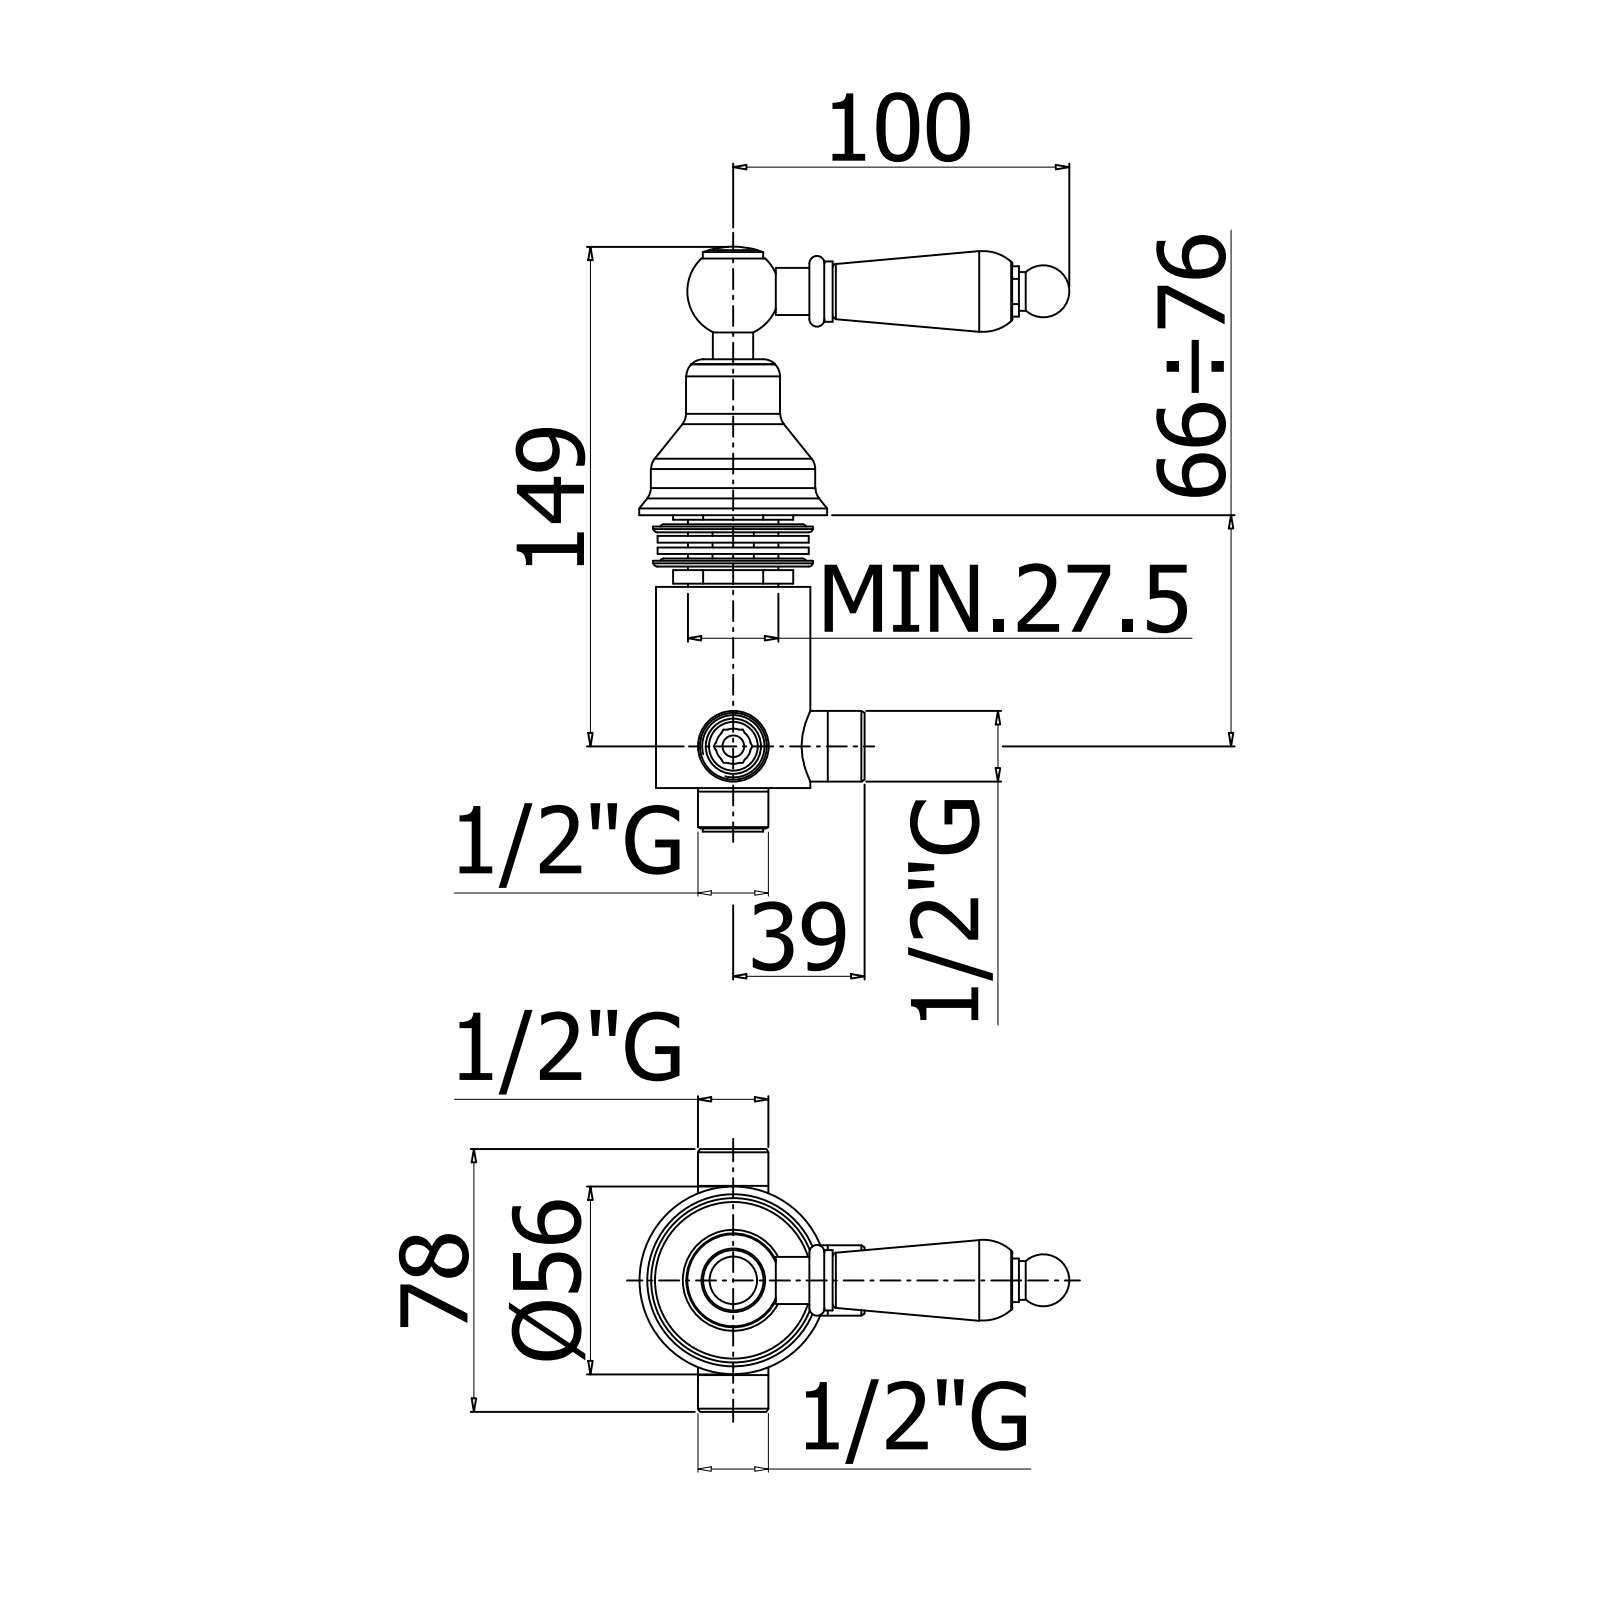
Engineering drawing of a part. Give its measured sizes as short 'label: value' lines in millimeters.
name: ZDEV083CR
written by: CREO PARAMETRIC BY PTC INC, 2020044 (CONFIG_CONTROL_DESIGN)
unit: mm
bodies: 5 solids, 227 faces (80 planar, 46 cylindrical, 101 other)
size: 125.7 × 85.3 × 55
volume: 53 684 mm³; area: 28 071 mm²
holes: 1× ⌀6.2, 1× ⌀9, 1× ⌀11.5, 1× ⌀14.9, 1× ⌀16.2, 1× ⌀25.7, 1× ⌀27.4, 1× ⌀45, 1× ⌀52.8
bosses: 1× ⌀55, 1× ⌀49, 1× ⌀42.6, 1× ⌀29.5, 1× ⌀28, 1× ⌀19, 1× ⌀18, 1× ⌀14
face distances: 0.6, 4, 9.4, 2, 44, 43.4, 5.68, 16, 2.6, 6.6
